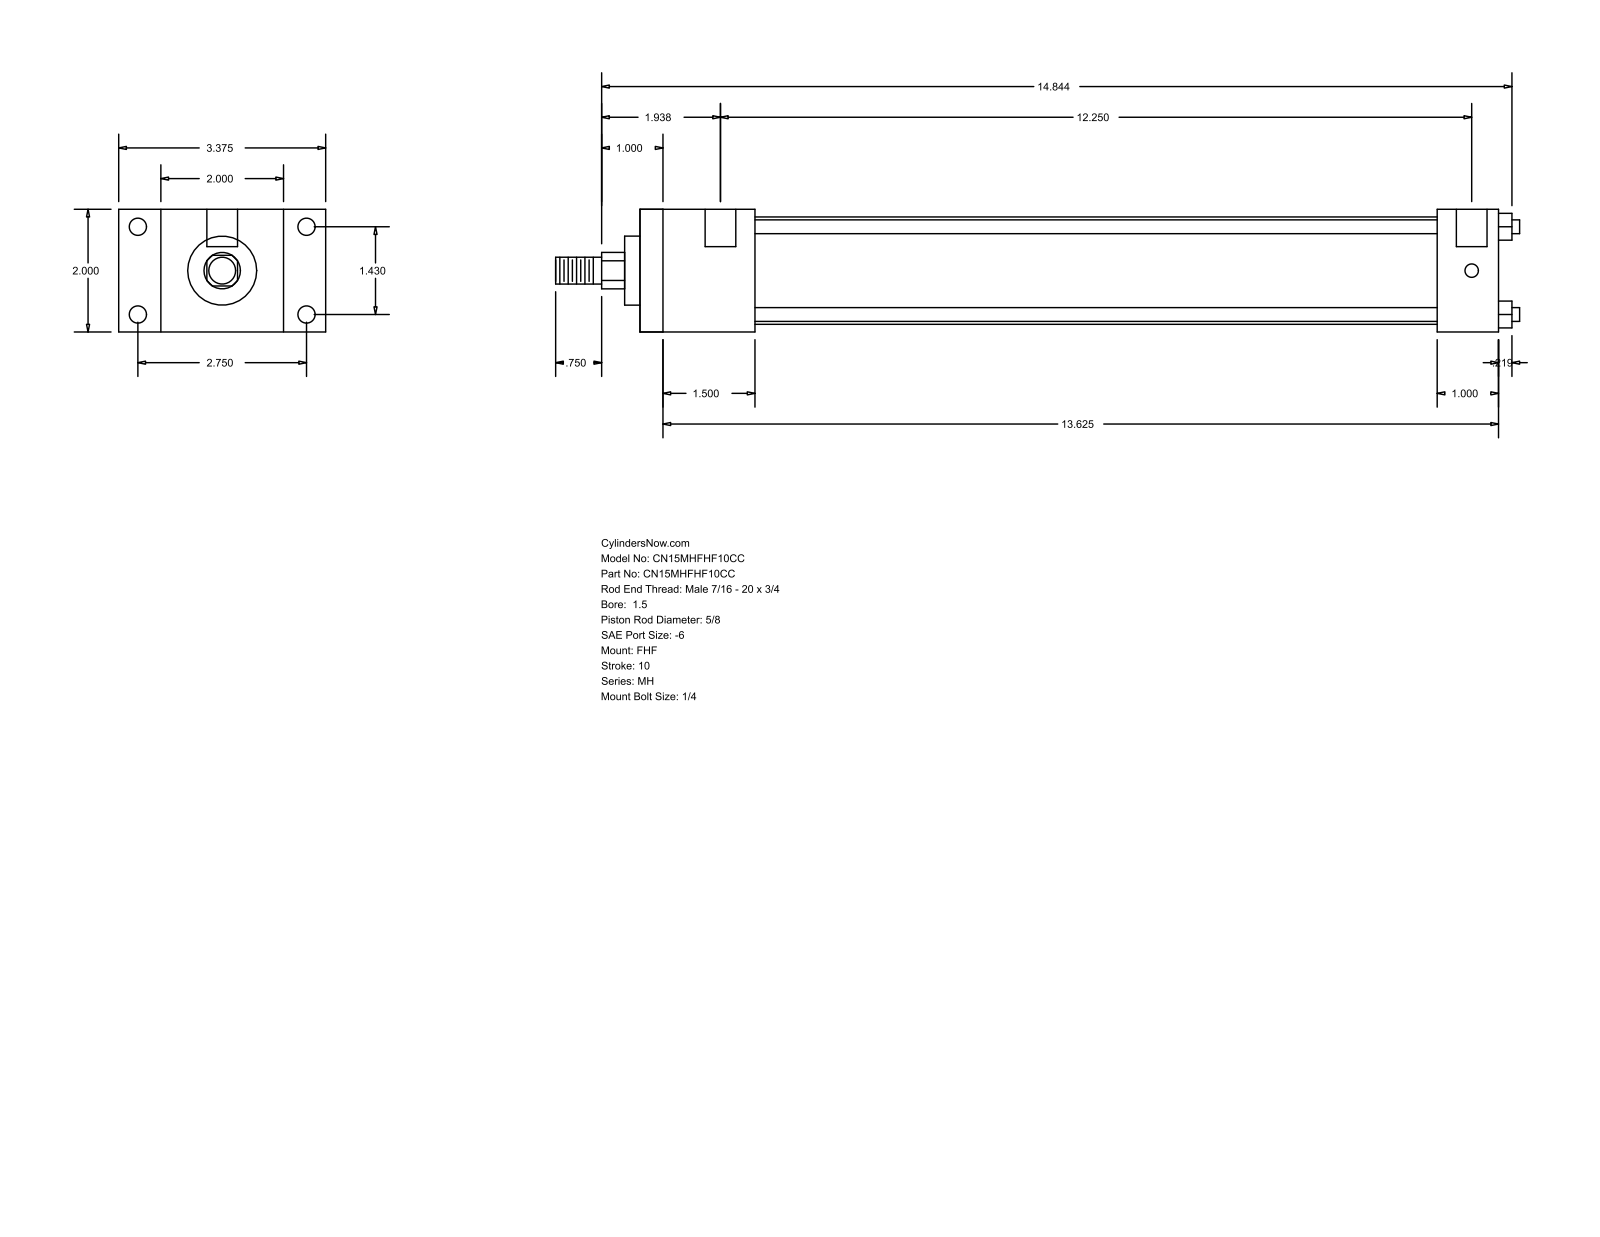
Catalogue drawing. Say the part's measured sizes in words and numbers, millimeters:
The part is named "MH_FHF__0150_0.625". Its 3-D file was written by "GSSL Pune (CONFIG_CONTROL_DESIGN)". It is 0 solids with 88 faces: 60 planar, 28 cylindrical and 0 other. Overall it measures 399.26 by 85.72 by 50.8 millimeters. Round holes: 4 of diameter 5.56, 4 of diameter 7.14, 2 of diameter 12.7. Round bosses or shafts: 4 of diameter 5.71, 1 of diameter 44.45, 1 of diameter 28.57, 1 of diameter 15.88, 1 of diameter 11.11. Partial cylindrical surfaces (rounded edges, fillets, slot ends): 1 of radius 7.54. The main face-to-face distances are 50.8, 17.46, 68.26, 47.62, 85.72, 355.6, 307.98, 330.19, 282.57, 25.41. The hole center spacings are 36.32, 69.84, 78.72, 314.32, 3.17, 311.15.
